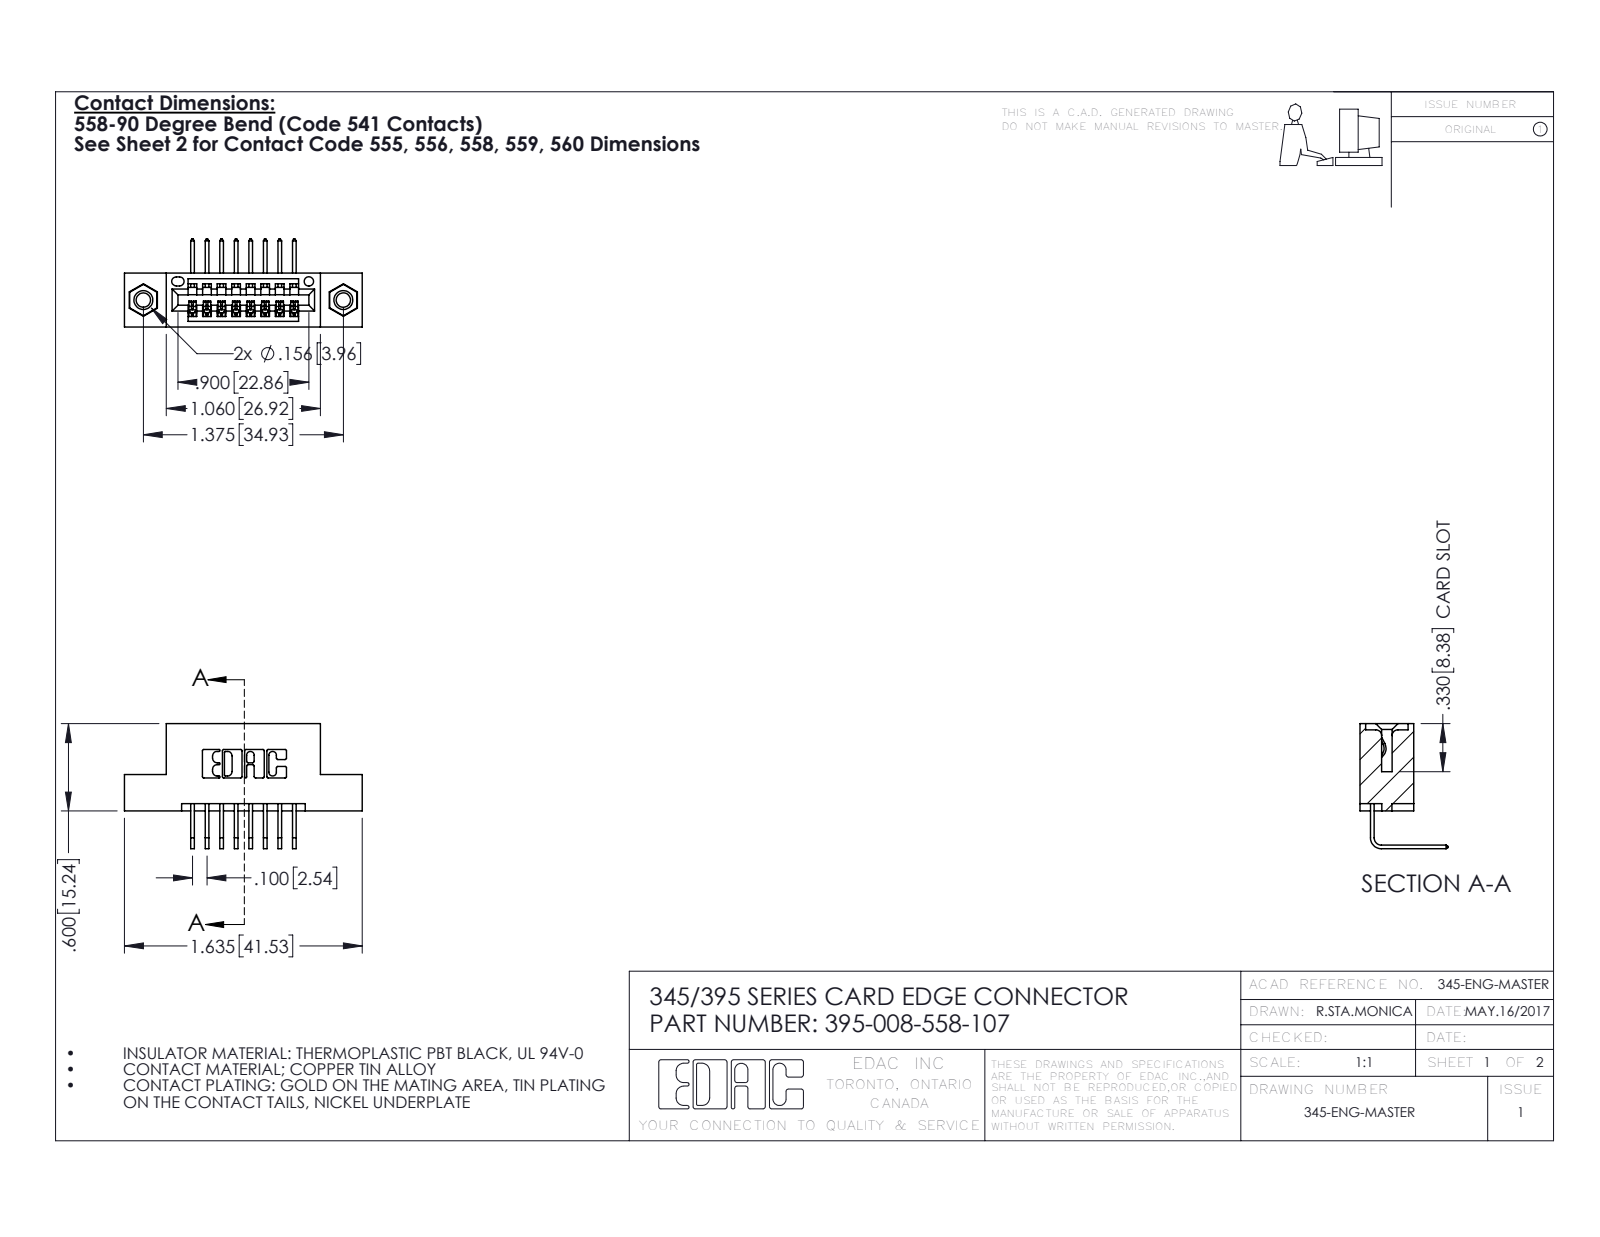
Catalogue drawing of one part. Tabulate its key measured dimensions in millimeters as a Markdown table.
| quantity | value |
| --- | --- |
| part name | 345-292-001_558 Tail - 2; 395-008-558-107; 345-250-001_345-250-005-103; 345 Part_Flush Mounting Lugs - 0.156 Dia-TI |
| STEP written by | SolidWorks 2016 (CONFIG_CONTROL_DESIGN) |
| units | millimeters |
| bodies | 11 solids, 666 faces (448 planar, 202 cylindrical, 16 other) |
| overall size | 41.5 × 21.8 × 15.4 |
| volume | 3 690 mm³ |
| surface area | 4 616 mm² |
| round holes (diameter × count) | 2.5 × 2, 3.2 × 2, 4 × 2, 1.6 × 1 |
| round bosses / shafts (diameter × count) | 3.9 × 2 |
| partial cylindrical surfaces (radius × count) | 0.3 × 22, 0.2 × 16, 0.2 × 6, 0.8 × 6, 0.7 × 3, 0.8 × 2, 1 × 2, 0.4 × 1 |
| main face-to-face distances | 5.1, 9.4, 2.5, 1.8, 7.6, 7.6, 2.5, 6.9, 0.6, 1.5 |
| hole center spacings | 6.9, 29.1, 34.9 |
